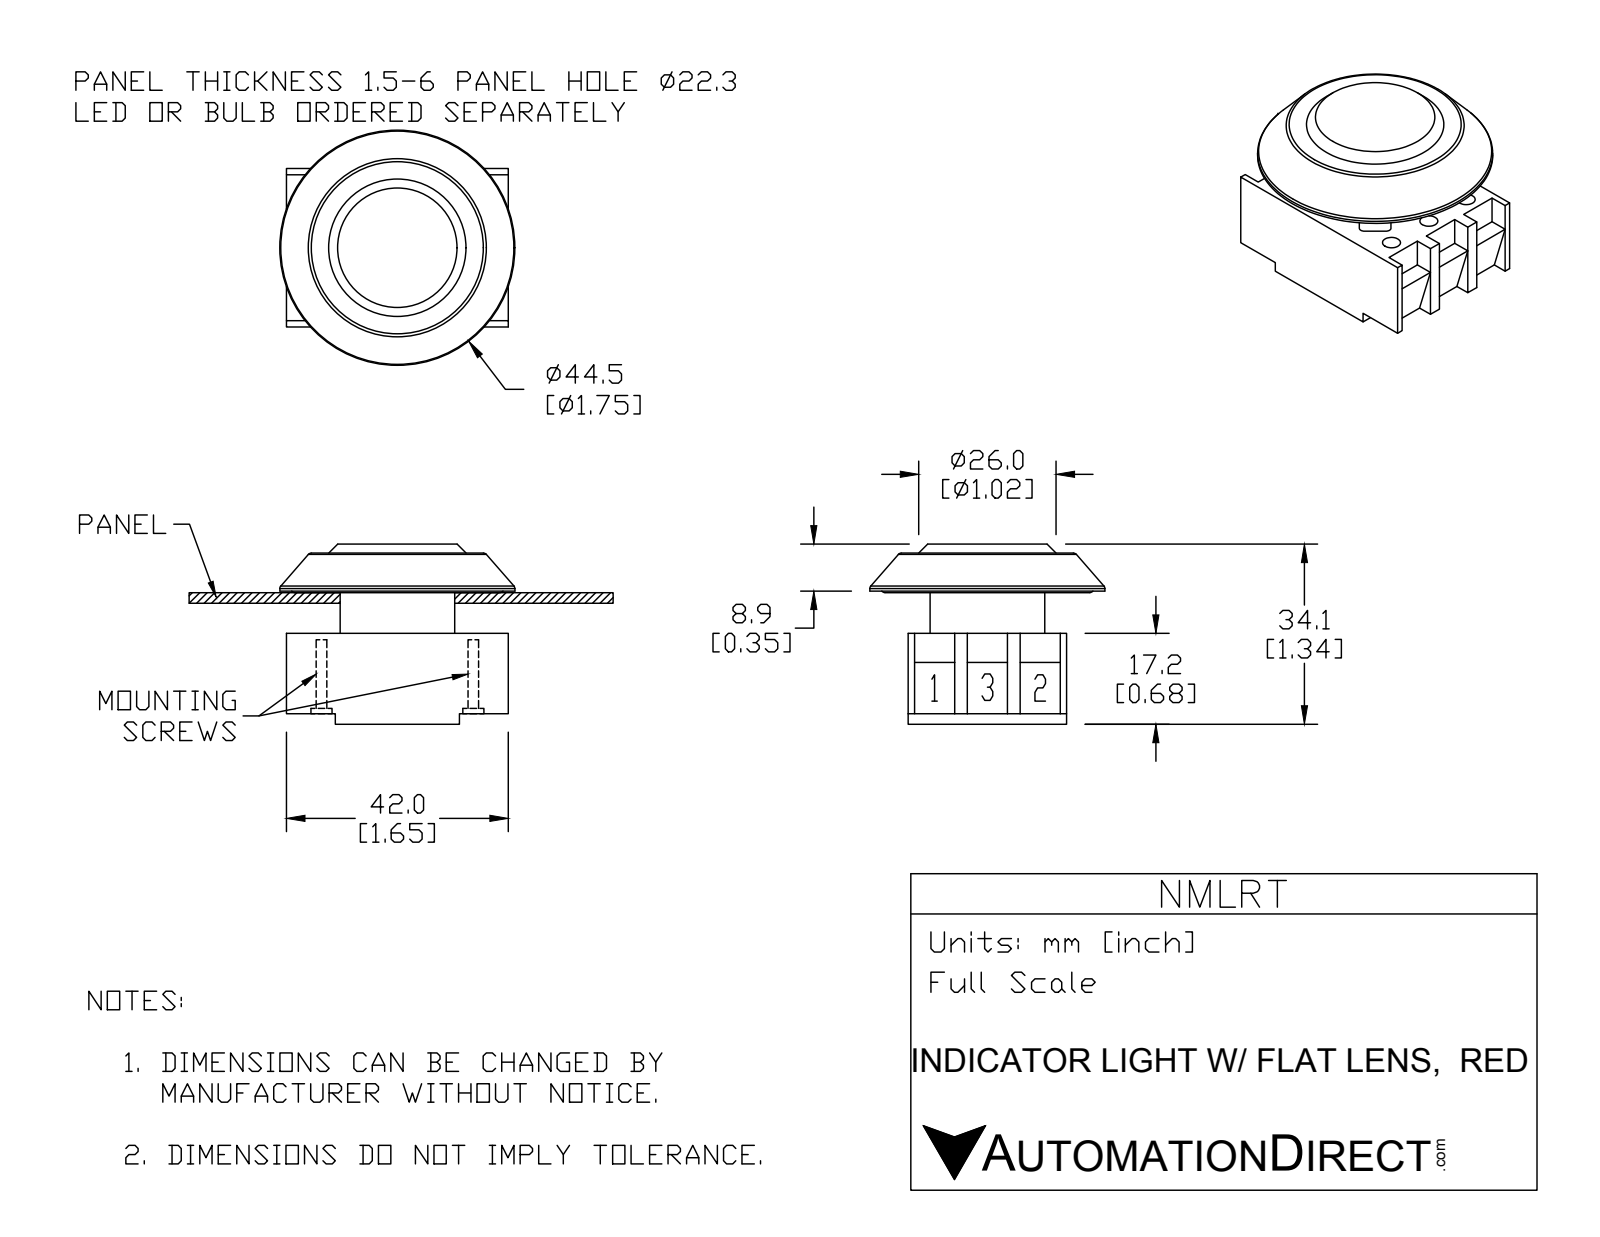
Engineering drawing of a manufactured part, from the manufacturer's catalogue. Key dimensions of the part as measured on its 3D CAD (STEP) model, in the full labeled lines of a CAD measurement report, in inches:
Part name (STEP PRODUCT): NMLRT
STEP written by: SolidWorks 2015 (AUTOMOTIVE_DESIGN)
Units: inches
Bodies: 6 solids, 209 faces (125 planar, 63 cylindrical, 21 other)
Overall size (bounding box): 1.752 × 1.752 × 1.343
Volume: 1.461 in³ · Surface area: 23.46 in²
Round holes (diameter × count): ⌀0.134 ×6, ⌀0.197 ×6, ⌀0.492 ×1
Round bosses / shafts (diameter × count): ⌀0.181 ×2, ⌀0.157 ×2, ⌀1.752 ×1, ⌀0.854 ×1
Partial cylindrical surfaces — rounded edges, fillets, slot ends (radius × count): R0.039 ×8, R0.343 ×5, R0.433 ×1
Main face-to-face distances: 1.181, 0.598, 0.315, 0.303, 0.362, 0.665, 0.35, 0.902, 0.394, 0.295
Hole centre spacings: 0.394, 0.69, 1.199, 1.132, 0.566, 0.787, 1.379
